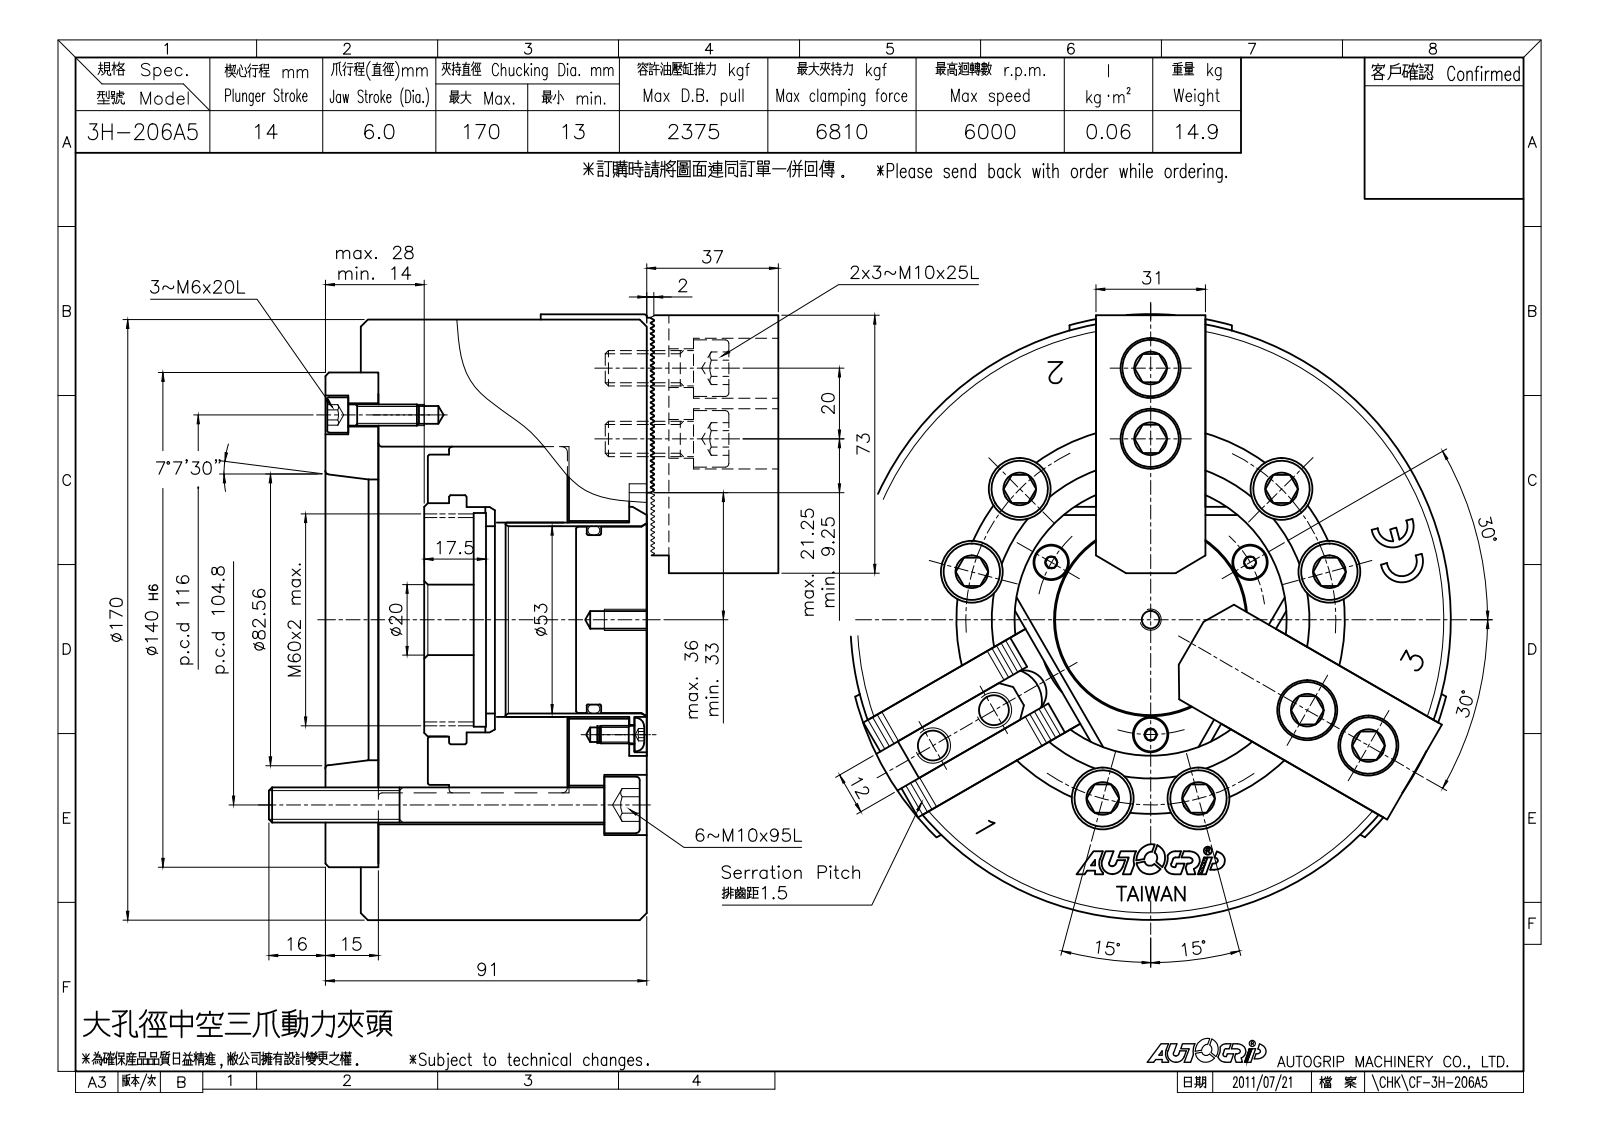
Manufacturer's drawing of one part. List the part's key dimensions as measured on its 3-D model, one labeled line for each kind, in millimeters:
Part name (STEP PRODUCT): CF-3H-206-06000; SJ-06; M10x25; CF-3H-206-02010 (+6 more)
STEP written by: SolidWorks 2016 (CONFIG_CONTROL_DESIGN)
Units: millimetres
Bodies: 27 solids, 1362 faces (921 planar, 330 cylindrical, 111 other)
Overall size (bounding box): 171.22 × 170 × 143
Volume: 1 874 000 mm³ · Surface area: 304 709 mm²
Round holes (diameter × count): ⌀11 ×20, ⌀12 ×12, ⌀5 ×6, ⌀6.6 ×6, ⌀17 ×6, ⌀17.5 ×6, ⌀4.2 ×3, ⌀5.5 ×3, ⌀10 ×3, ⌀16.5 ×3, ⌀45 ×1, ⌀53 ×1
Round bosses / shafts (diameter × count): ⌀10 ×15, ⌀16 ×12, ⌀9.5 ×3, ⌀6 ×3, ⌀5 ×3, ⌀170 ×1, ⌀63.8 ×1, ⌀54 ×1
Partial cylindrical surfaces — rounded edges, fillets, slot ends (radius × count): R0.1 ×147, R6 ×4
Main face-to-face distances: 76, 15, 5, 58.5, 31, 56, 20, 10, 36, 91
Hole centre spacings: 27.12, 52.39, 42.56, 90.74, 52.4, 67.35, 101.21, 15.44
